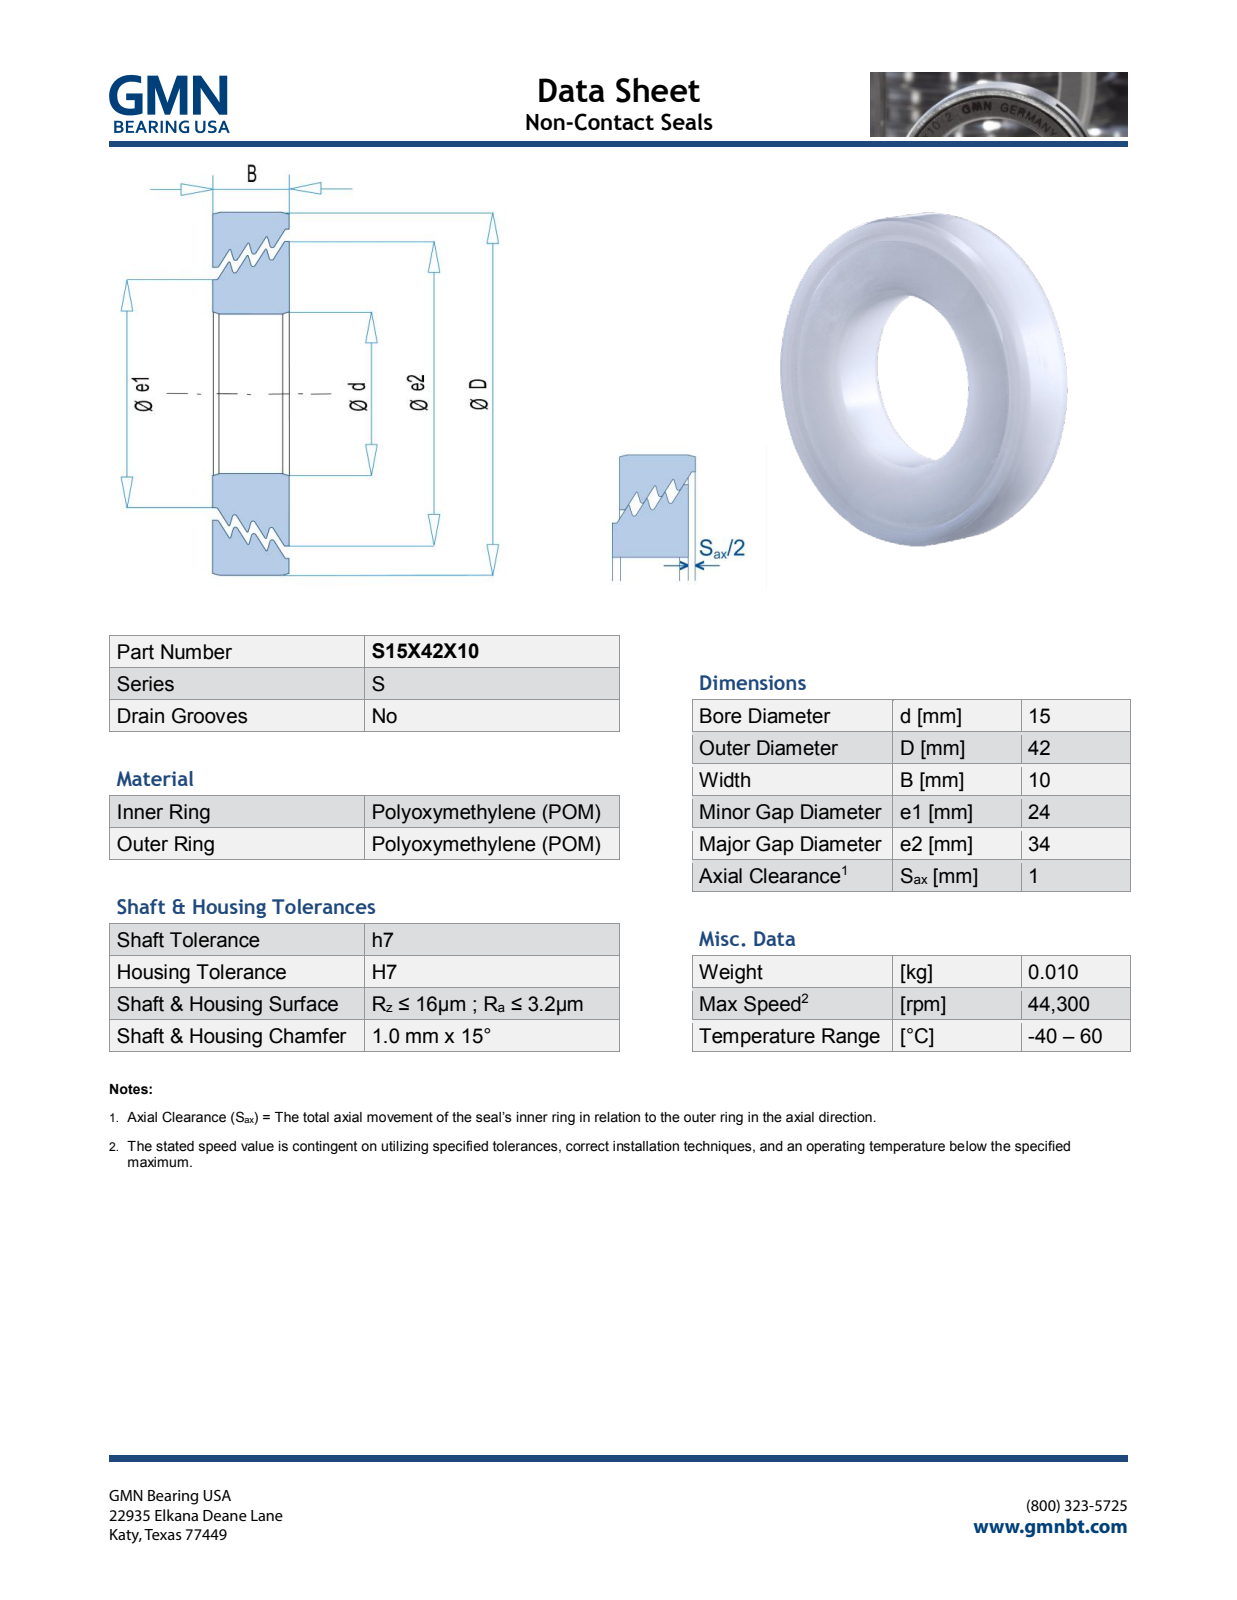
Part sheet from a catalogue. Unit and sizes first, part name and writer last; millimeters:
Units: millimetres
Overall size (bounding box): 42 × 42 × 10.07
Round holes (diameter × count): ⌀15 ×1, ⌀25.63 ×1, ⌀35.63 ×1
Round bosses / shafts (diameter × count): ⌀42 ×1, ⌀34 ×1, ⌀24 ×1
Main face-to-face distances: 10, 10.07, 0.32, 0.33, 2.58, 2.26, 1.83, 2.25, 2.15, 1.93
Volume: 11 278 mm³ · Surface area: 7 855 mm²
Bodies: 2 solids, 587 faces (507 planar, 12 cylindrical, 68 other)
Part name (STEP PRODUCT): S15X42X10_PRT
STEP written by: PRO/ENGINEER BY PARAMETRIC TECHNOLOGY CORPORATION, 2013150 (AUTOMOTIVE_DESIGN)
